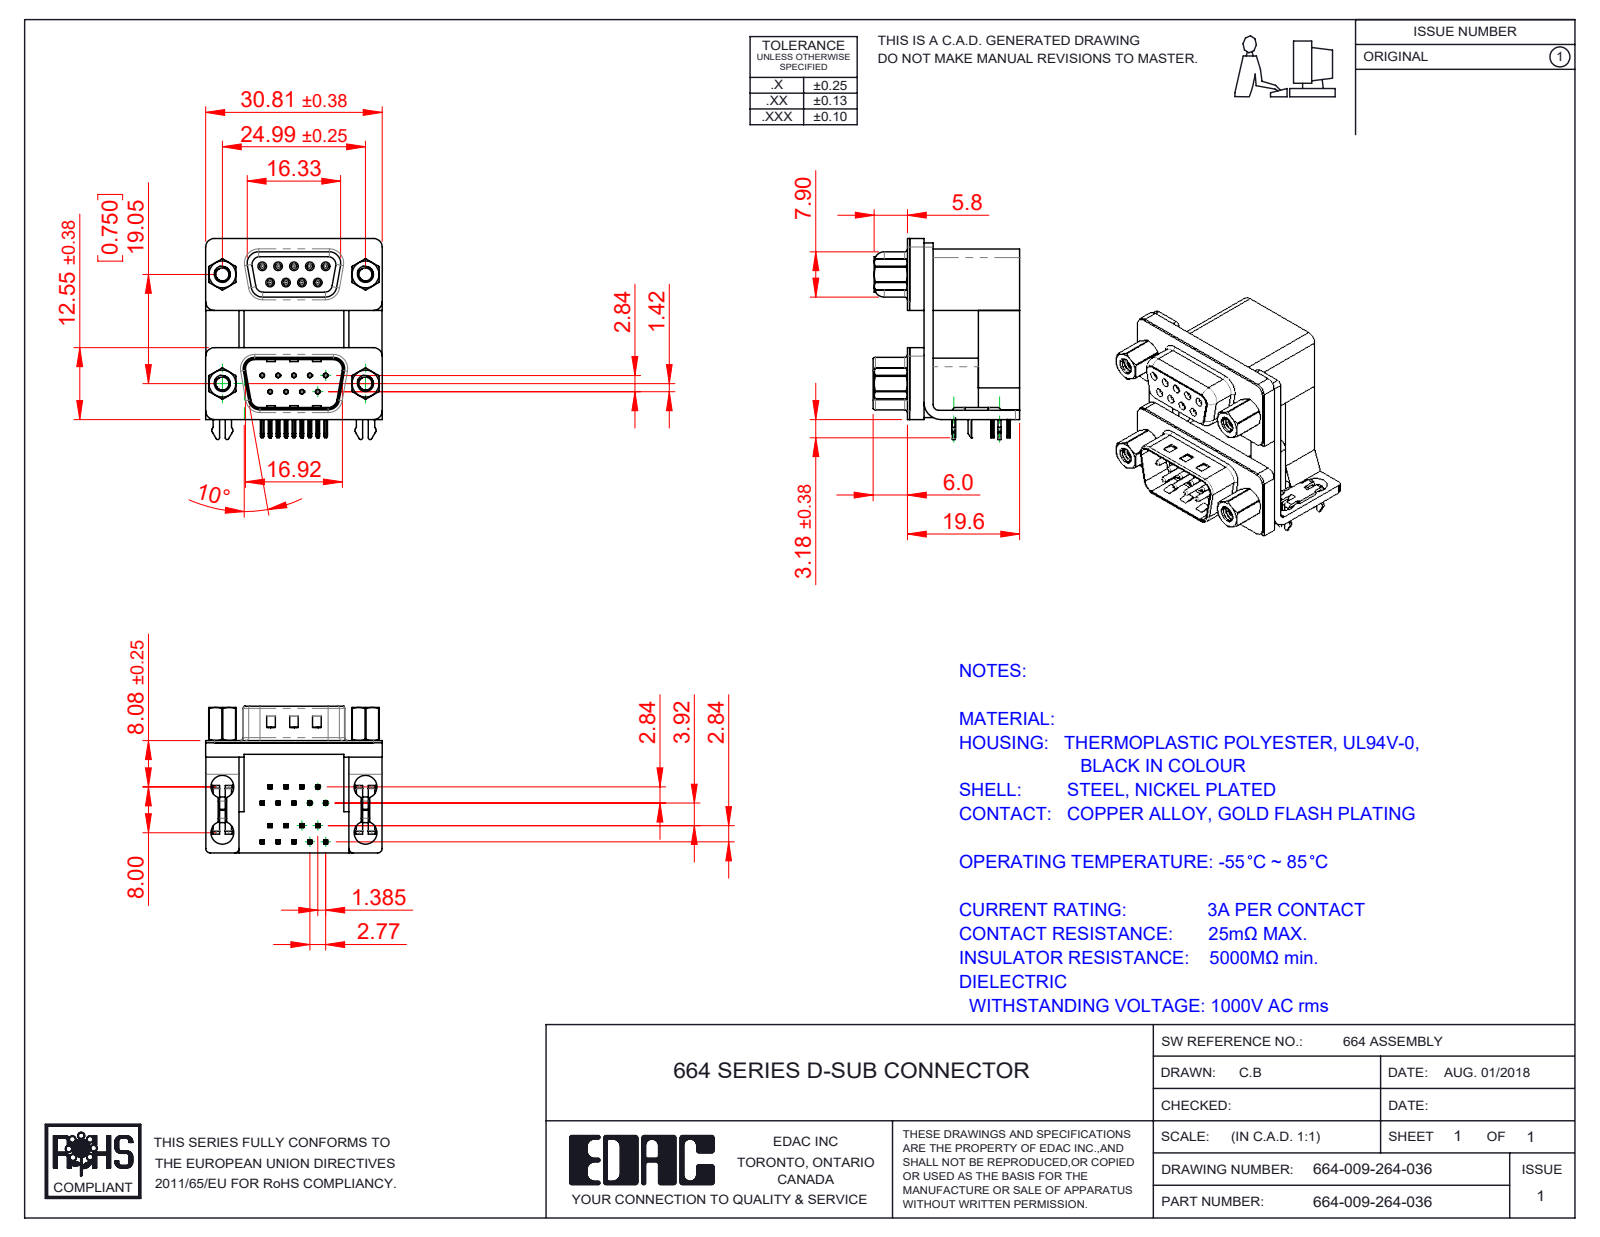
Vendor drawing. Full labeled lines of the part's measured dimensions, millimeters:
Part name (STEP PRODUCT): 664 2 Prong Board Lock_3; 664 4-40 Hex Standoff 5; 664 Housing Spacer_09 Contacts M; 664 Housing Lower_09 Contacts (+8 more)
STEP written by: SolidWorks 2020 (CONFIG_CONTROL_DESIGN)
Units: millimetres
Bodies: 35 solids, 2933 faces (1409 planar, 889 cylindrical, 635 other)
Overall size (bounding box): 35.1 × 30.81 × 25.6
Volume: 11 206 mm³ · Surface area: 13 763 mm²
Round holes (diameter × count): ⌀0.8 ×18, ⌀0.35 ×9, ⌀0.9 ×9, ⌀4 ×8, ⌀2.26 ×4, ⌀2.29 ×4, ⌀3.5 ×4, ⌀4.8 ×4, ⌀5 ×4
Round bosses / shafts (diameter × count): ⌀1.2 ×9, ⌀0.75 ×9, ⌀4.9 ×4, ⌀4.75 ×4, ⌀3.9 ×4, ⌀2.79 ×4
Partial cylindrical surfaces — rounded edges, fillets, slot ends (radius × count): R0.1 ×74, R0.25 ×46, R0.15 ×36, R0.12 ×18, R0.35 ×18, R0.5 ×16, R1.5 ×13, R0.75 ×10
Main face-to-face distances: 0.4, 2.5, 16.7, 19.2, 7.2, 9.5, 12, 19.6, 12.4, 2.9
Hole centre spacings: 3.16, 2.77, 19.25, 19.05, 5.54, 19.84, 16.27, 21.93
